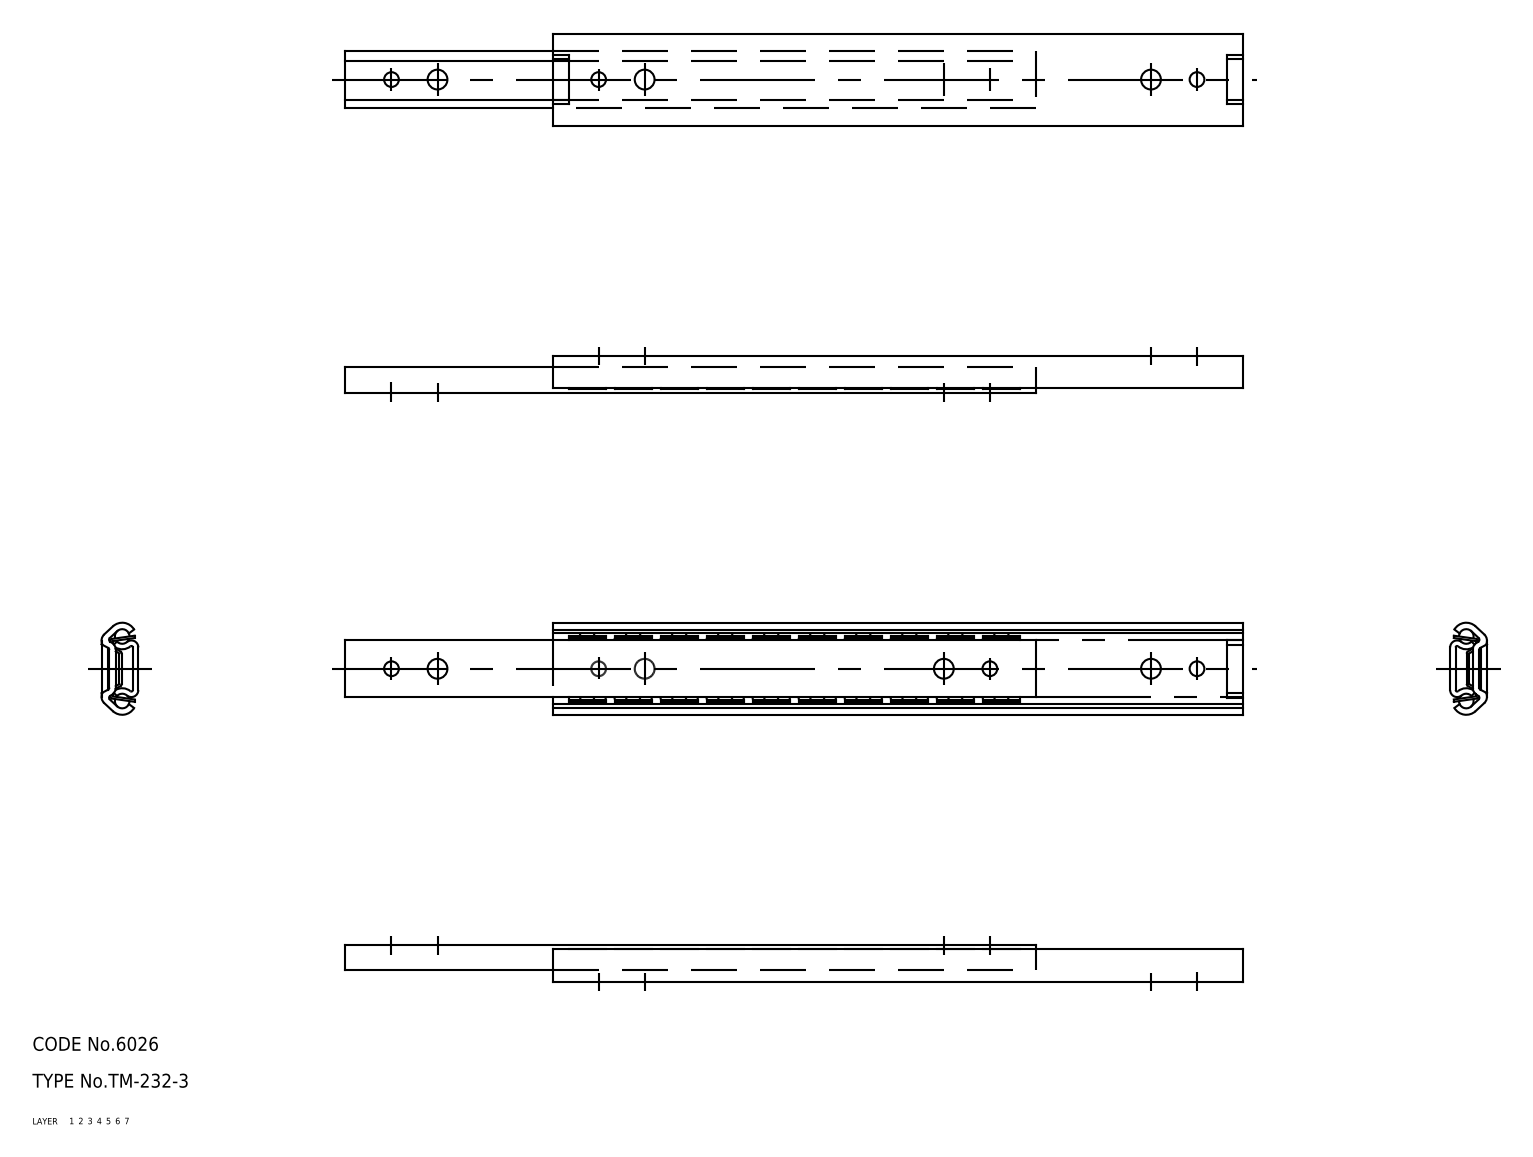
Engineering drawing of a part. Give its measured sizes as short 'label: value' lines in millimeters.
name: ball; retainer; member_B; member_A (+1 more)
written by: CADfix (AUTOMOTIVE_DESIGN)
unit: mm
bodies: 23 solids, 310 faces (0 planar, 0 cylindrical, 310 other)
size: 195 × 20 × 8
volume: 10 531 mm³; area: 20 265 mm²
